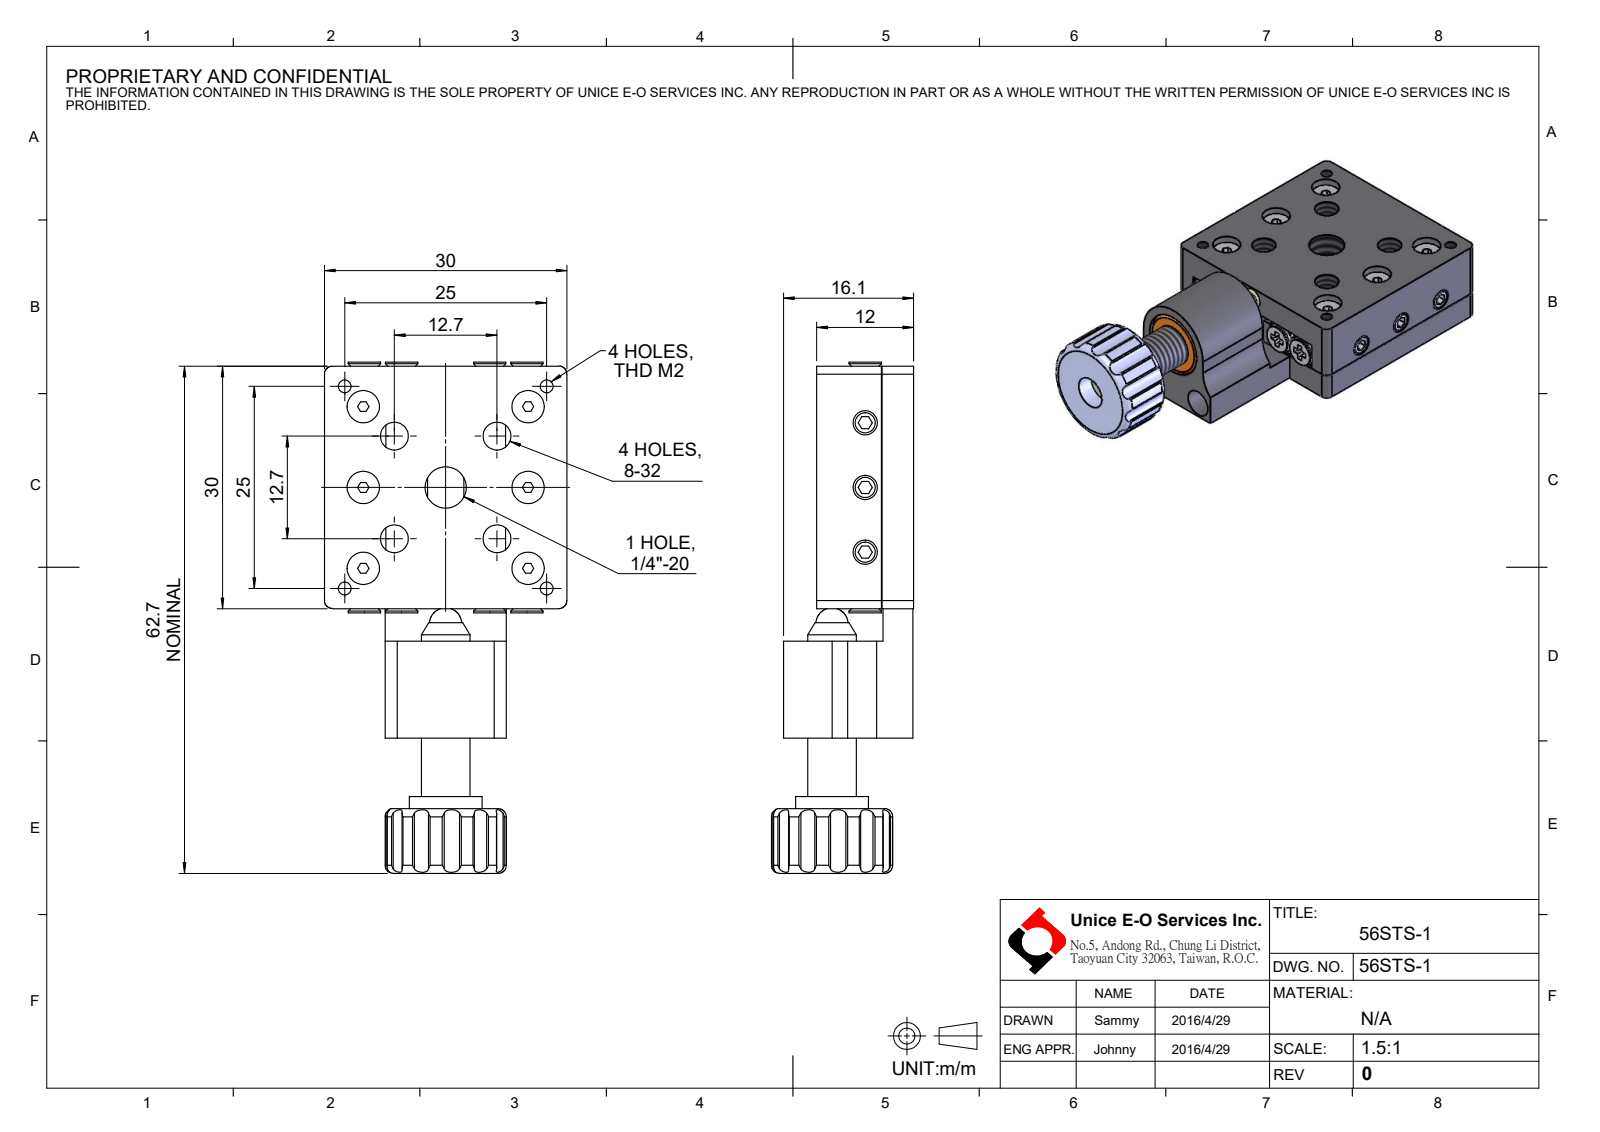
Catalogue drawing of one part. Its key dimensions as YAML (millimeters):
part_name: "56STS-1"
step_written_by: "SolidWorks 2022 (CONFIG_CONTROL_DESIGN)"
units: millimeters
bodies: {solids: 0, faces: 476, planar: 284, cylindrical: 156, other: 36}
overall_size: [62.4, 30, 17.59]
round_holes:
  - {diameter: 4, count: 14}
  - {diameter: 1.6, count: 4}
  - {diameter: 2.5, count: 4}
  - {diameter: 3.45, count: 4}
  - {diameter: 4.7, count: 1}
  - {diameter: 5.11, count: 1}
  - {diameter: 9.5, count: 1}
round_bosses_or_shafts:
  - {diameter: 4, count: 4}
  - {diameter: 3, count: 3}
  - {diameter: 9, count: 1}
  - {diameter: 6, count: 1}
partial_cylinders:
  - {radius: 0.3, count: 24}
  - {radius: 1.5, count: 12}
  - {radius: 1, count: 4}
  - {radius: 5, count: 2}
  - {radius: 6, count: 1}
  - {radius: 7.5, count: 1}
face_to_face_distances: [3.9, 4, 8, 8.1, 12, 4.1, 30, 4.2, 11.5, 18.5]
hole_center_spacings: [10, 11.14, 18.45, 19.83, 4.9, 15.5, 3.4, 3.8]
